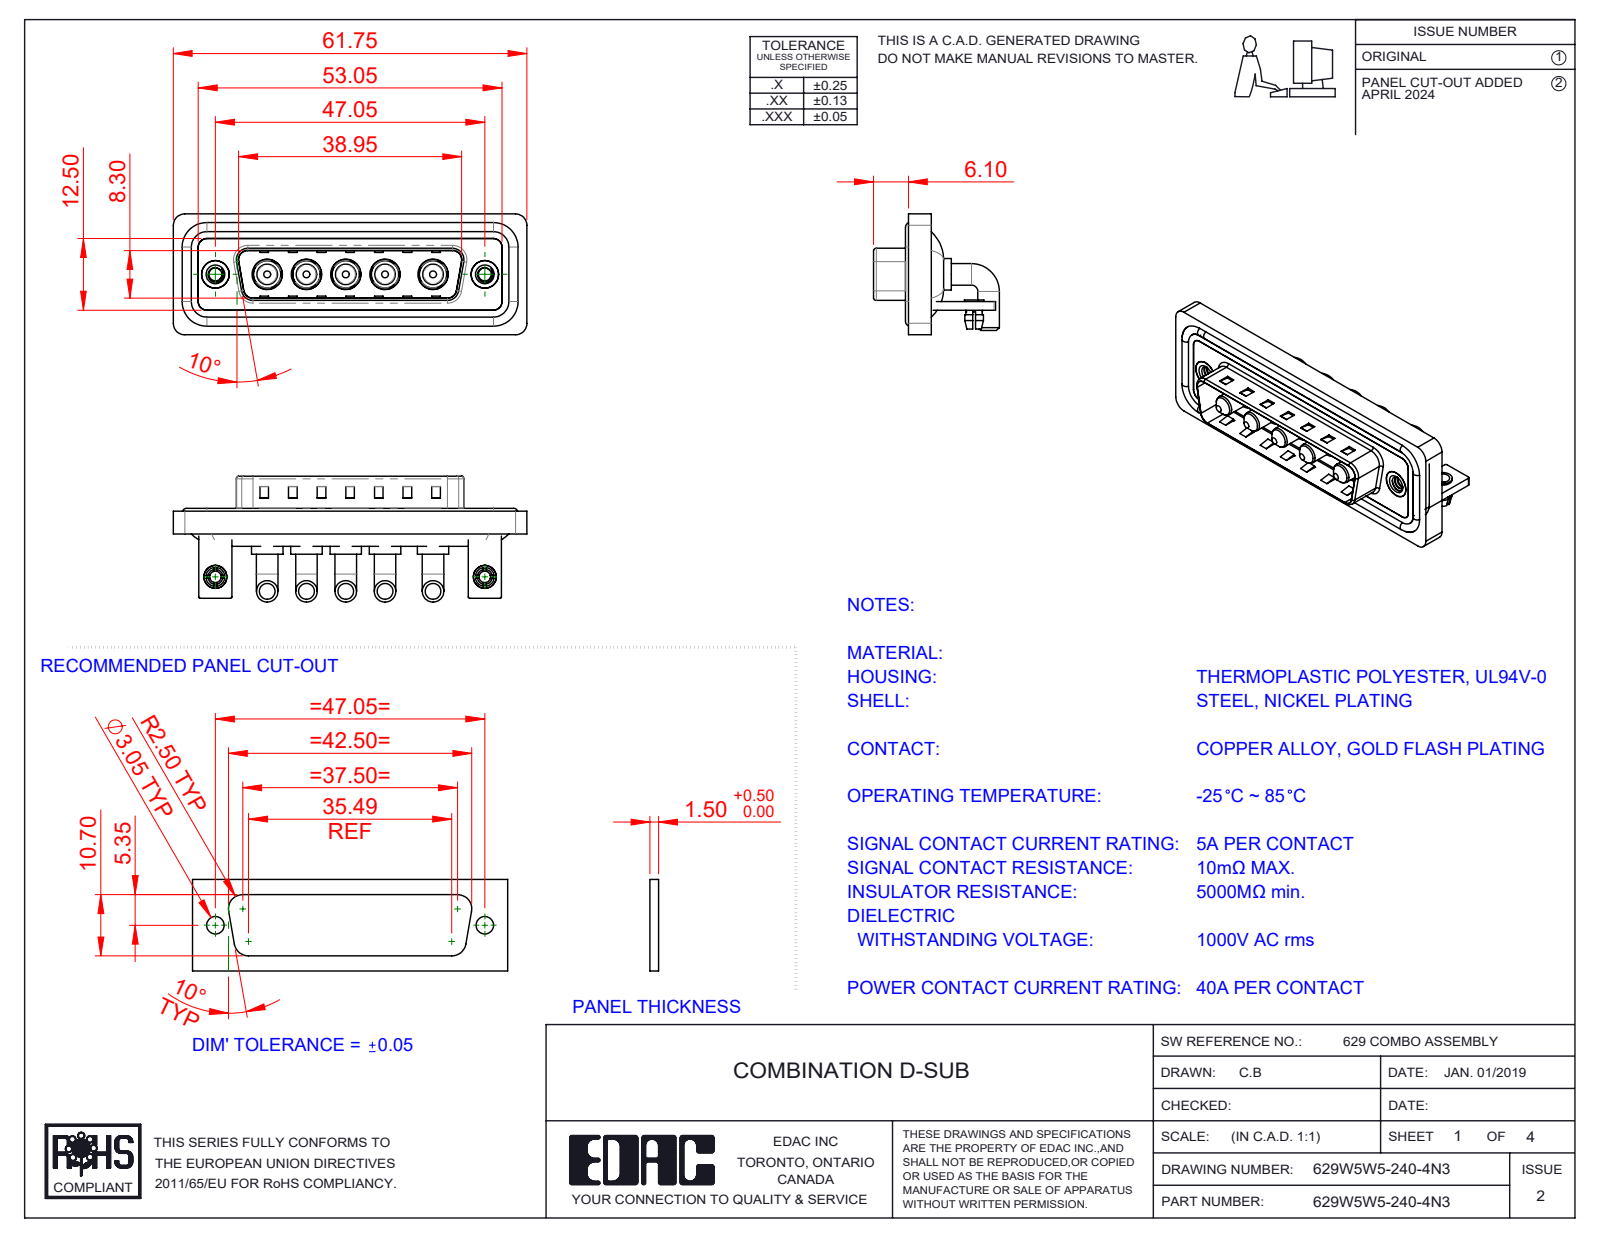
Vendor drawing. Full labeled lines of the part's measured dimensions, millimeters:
Part name (STEP PRODUCT): 629Combo Board Lock; 629Combo Stabilizer Bracket; 629W5W5-240-4N3; 629Combo Threaded Rivet_3 (+5 more)
STEP written by: SolidWorks 2023 (CONFIG_CONTROL_DESIGN)
Units: millimetres
Bodies: 21 solids, 830 faces (327 planar, 343 cylindrical, 160 other)
Overall size (bounding box): 61.75 × 21.98 × 21.1
Volume: 8 480 mm³ · Surface area: 13 289 mm²
Round holes (diameter × count): ⌀4.85 ×5, ⌀5.3 ×5, ⌀2 ×2, ⌀2.26 ×2, ⌀2.5 ×2, ⌀3.2 ×2, ⌀4 ×2, ⌀4.8 ×2, ⌀5 ×2
Round bosses / shafts (diameter × count): ⌀3.75 ×10, ⌀5.5 ×5, ⌀5.2 ×5, ⌀4.75 ×5, ⌀3.6 ×5, ⌀1.6 ×4, ⌀4.9 ×2, ⌀4 ×2
Partial cylindrical surfaces — rounded edges, fillets, slot ends (radius × count): R2 ×19, R1.5 ×18, R0.25 ×16, R0.5 ×9, R1.6 ×8, R2.1 ×5, R0.6 ×4, R0.65 ×4
Main face-to-face distances: 0.4, 1.5, 2.9, 0.8, 2.1, 1.1, 3.7, 4.5, 4.1, 1.2
Hole centre spacings: 6.86, 13.73, 47.05, 6.85, 6.87, 8.37, 8.38, 9.04
